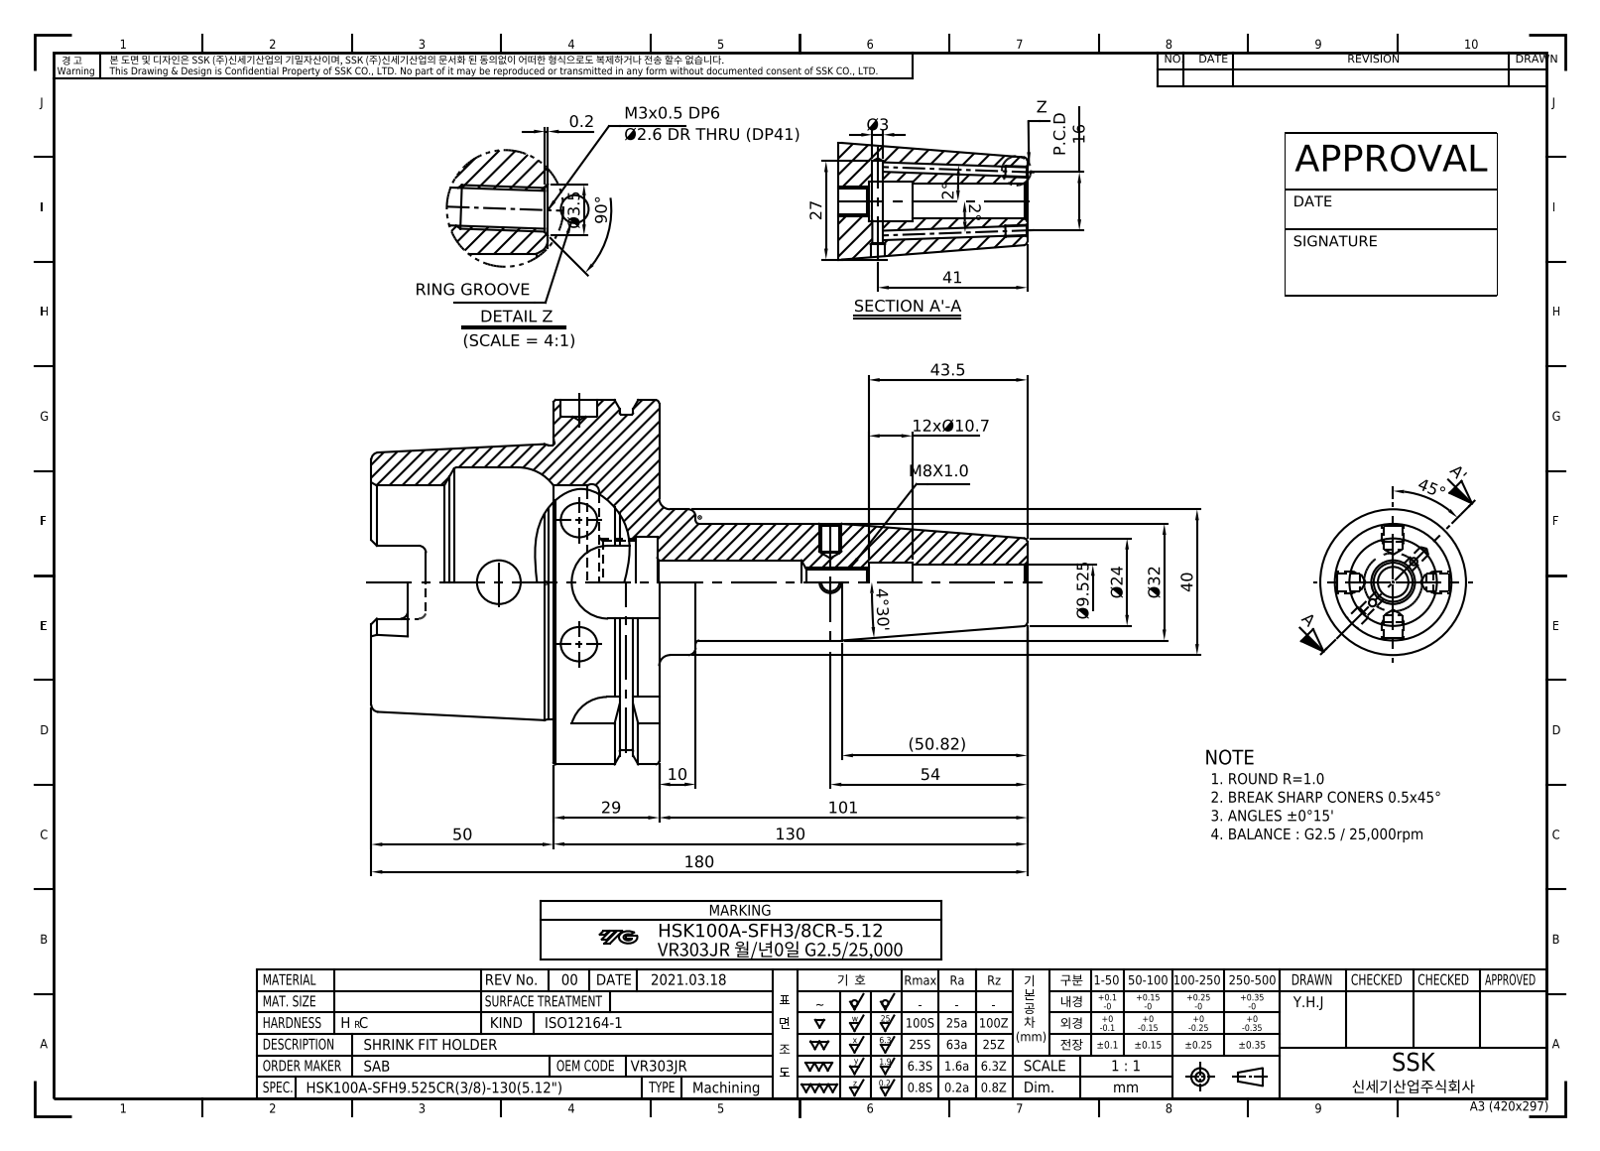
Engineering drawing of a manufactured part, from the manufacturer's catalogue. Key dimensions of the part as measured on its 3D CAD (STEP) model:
Part name (STEP PRODUCT): LO-HSK100A-SFH9.525CR-130
STEP written by: Autodesk Inventor 2022 (AUTOMOTIVE_DESIGN)
Units: millimetres
Bodies: 1 solid, 123 faces (39 planar, 38 cylindrical, 46 other)
Overall size (bounding box): 180 × 100 × 100
Volume: 321 784 mm³ · Surface area: 62 595 mm²
Round holes (diameter × count): ⌀2.46 ×2, ⌀12 ×2, ⌀6.92 ×1, ⌀9.52 ×1, ⌀10 ×1, ⌀10.72 ×1, ⌀22.38 ×1, ⌀25 ×1, ⌀53 ×1, ⌀63 ×1
Round bosses / shafts (diameter × count): ⌀100 ×1, ⌀92 ×1, ⌀75.41 ×1, ⌀40 ×1, ⌀32 ×1
Partial cylindrical surfaces — rounded edges, fillets, slot ends (radius × count): R2 ×6, R4.88 ×4, R10 ×4
Main face-to-face distances: 29, 12.5, 16.5, 79, 62.5, 50, 88, 10, 78.5, 28.5
